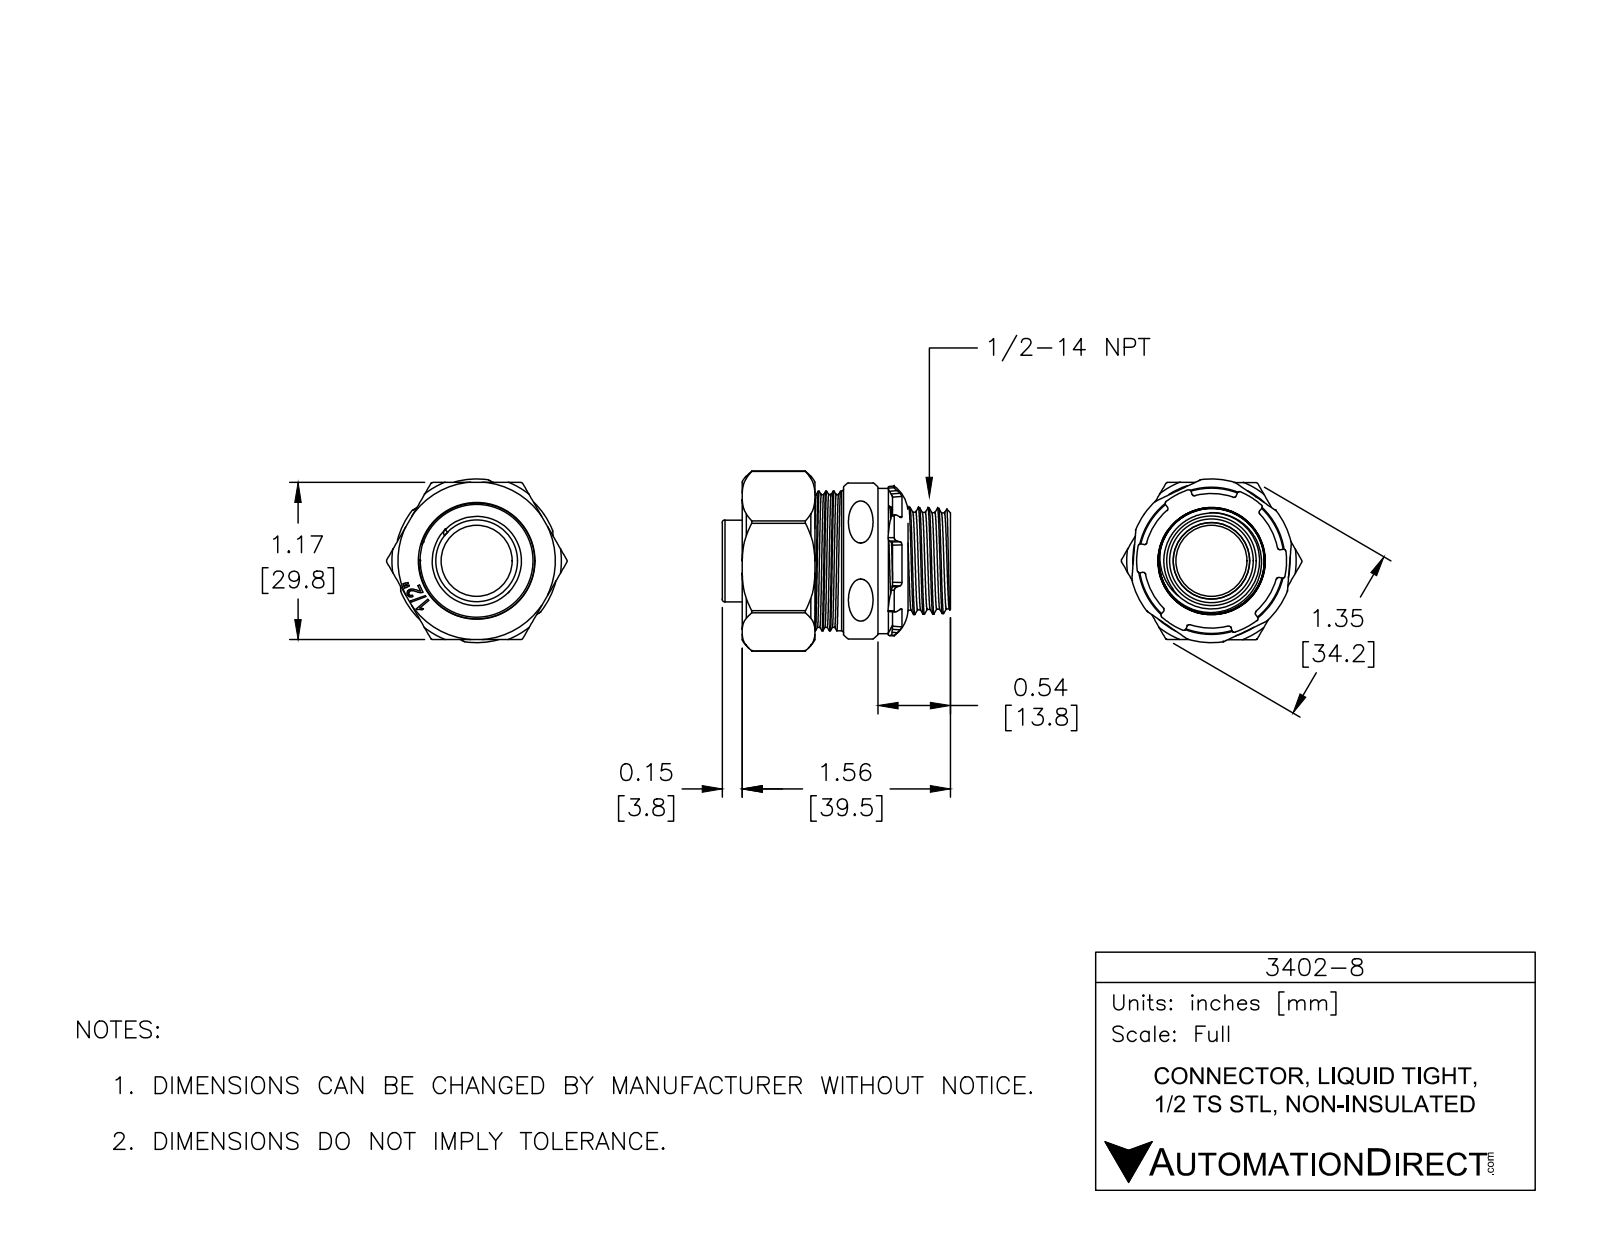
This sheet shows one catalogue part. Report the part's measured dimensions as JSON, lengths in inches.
{"part_name": "3402-8", "step_written_by": "SolidWorks 2018 (AUTOMOTIVE_DESIGN)", "units": "inches", "bodies": {"solids": 6, "faces": 497, "planar": 194, "cylindrical": 96, "other": 207}, "overall_size": [1.706, 1.344, 1.22], "volume_in3": 0.63, "surface_area_in2": 25.31, "round_holes": [[0.105, 1], [0.529, 1], [0.571, 1], [0.847, 1], [0.858, 1], [0.87, 1], [0.883, 1], [1.016, 1]], "round_bosses_or_shafts": [[1.083, 1], [1.043, 1], [0.992, 1], [0.886, 1], [0.61, 1], [0.569, 1], [0.086, 1]], "partial_cylinders_radius": [[0.007, 8], [0.02, 6], [0.034, 2], [0.009, 1], [0.013, 1], [0.025, 1], [0.334, 1]], "face_to_face_distances": [1.013, 1.092, 0.079, 1.173, 1.174, 1.173, 0.933, 0.08, 0.159, 0.543], "hole_center_spacings": [0.5]}
